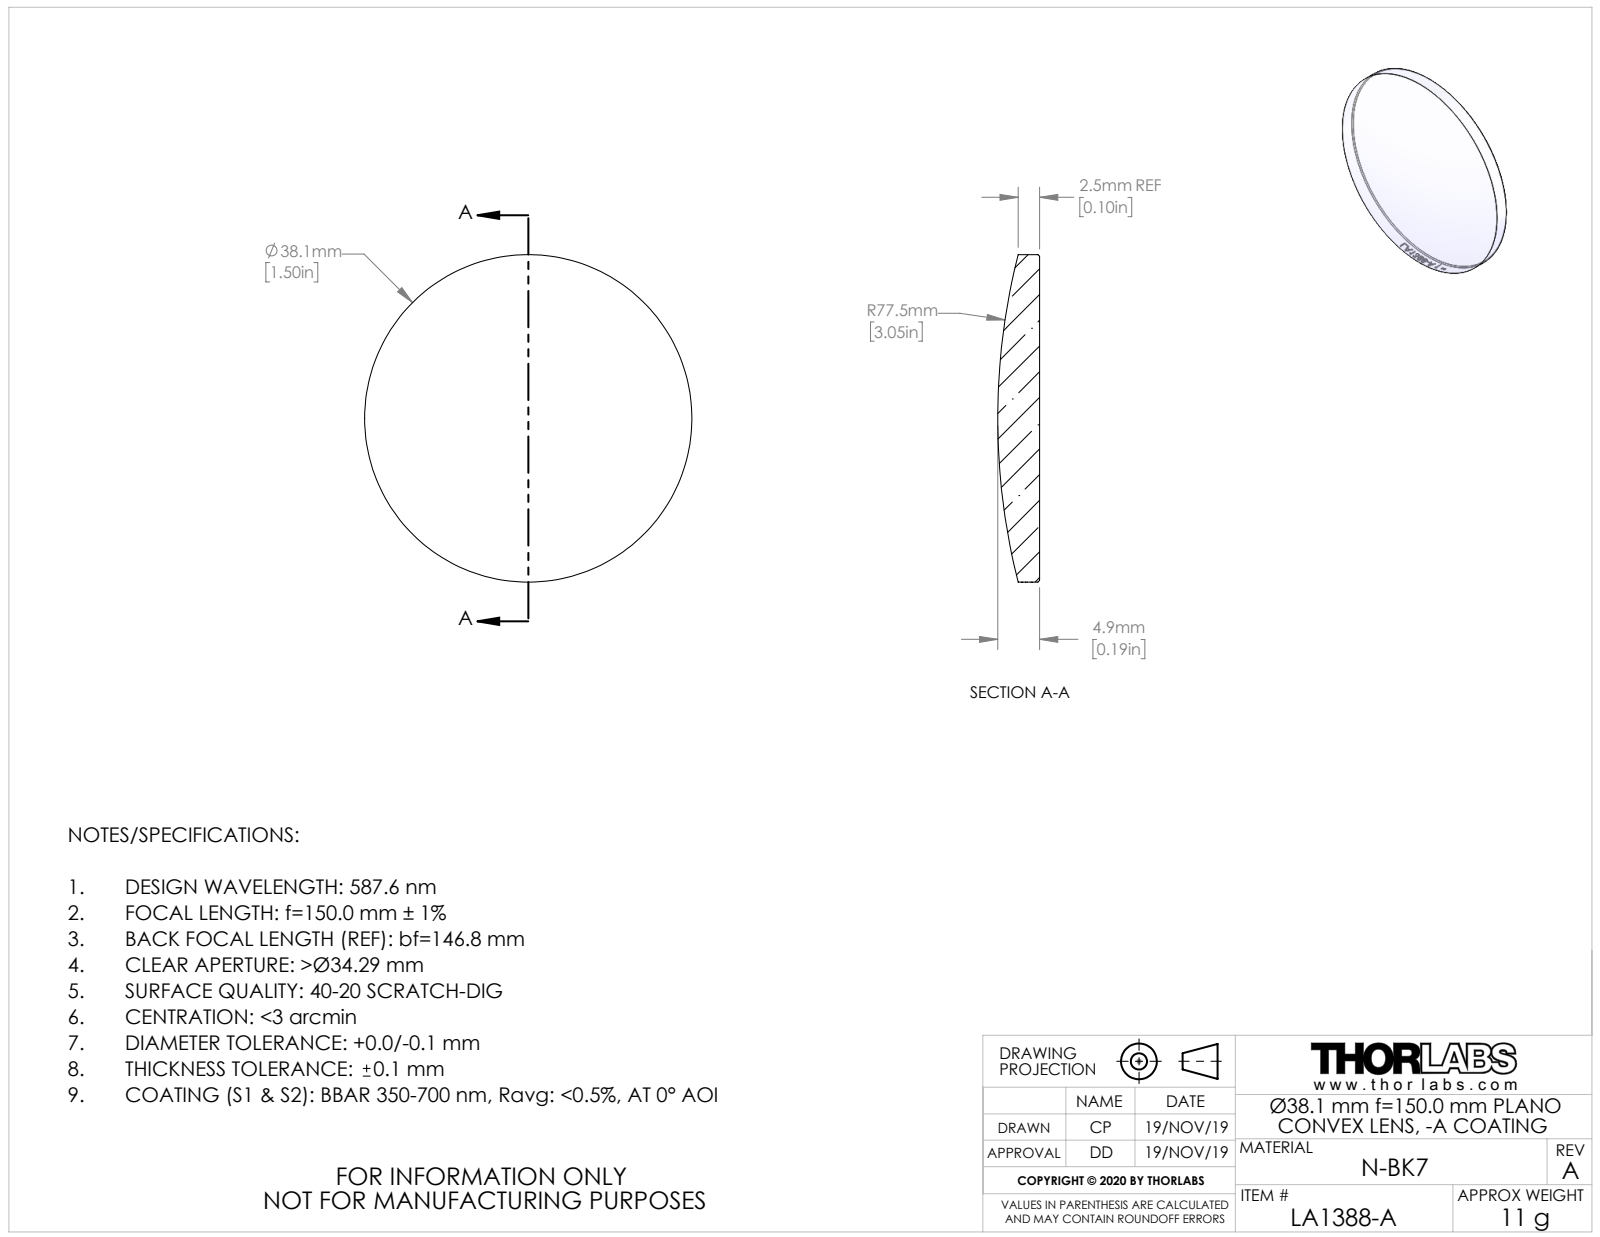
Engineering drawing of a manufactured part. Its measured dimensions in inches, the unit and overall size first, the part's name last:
Units: inches
Overall size (bounding box): 1.5 × 1.5 × 0.192
Round bosses / shafts (diameter × count): ⌀1.5 ×1
Volume: 0.257 in³ · Surface area: 4.004 in²
Bodies: 1 solid, 25 faces (1 planar, 20 cylindrical, 4 other)
Part name (STEP PRODUCT): TTN200713-E0W
STEP written by: SolidWorks 2018 (CONFIG_CONTROL_DESIGN)
